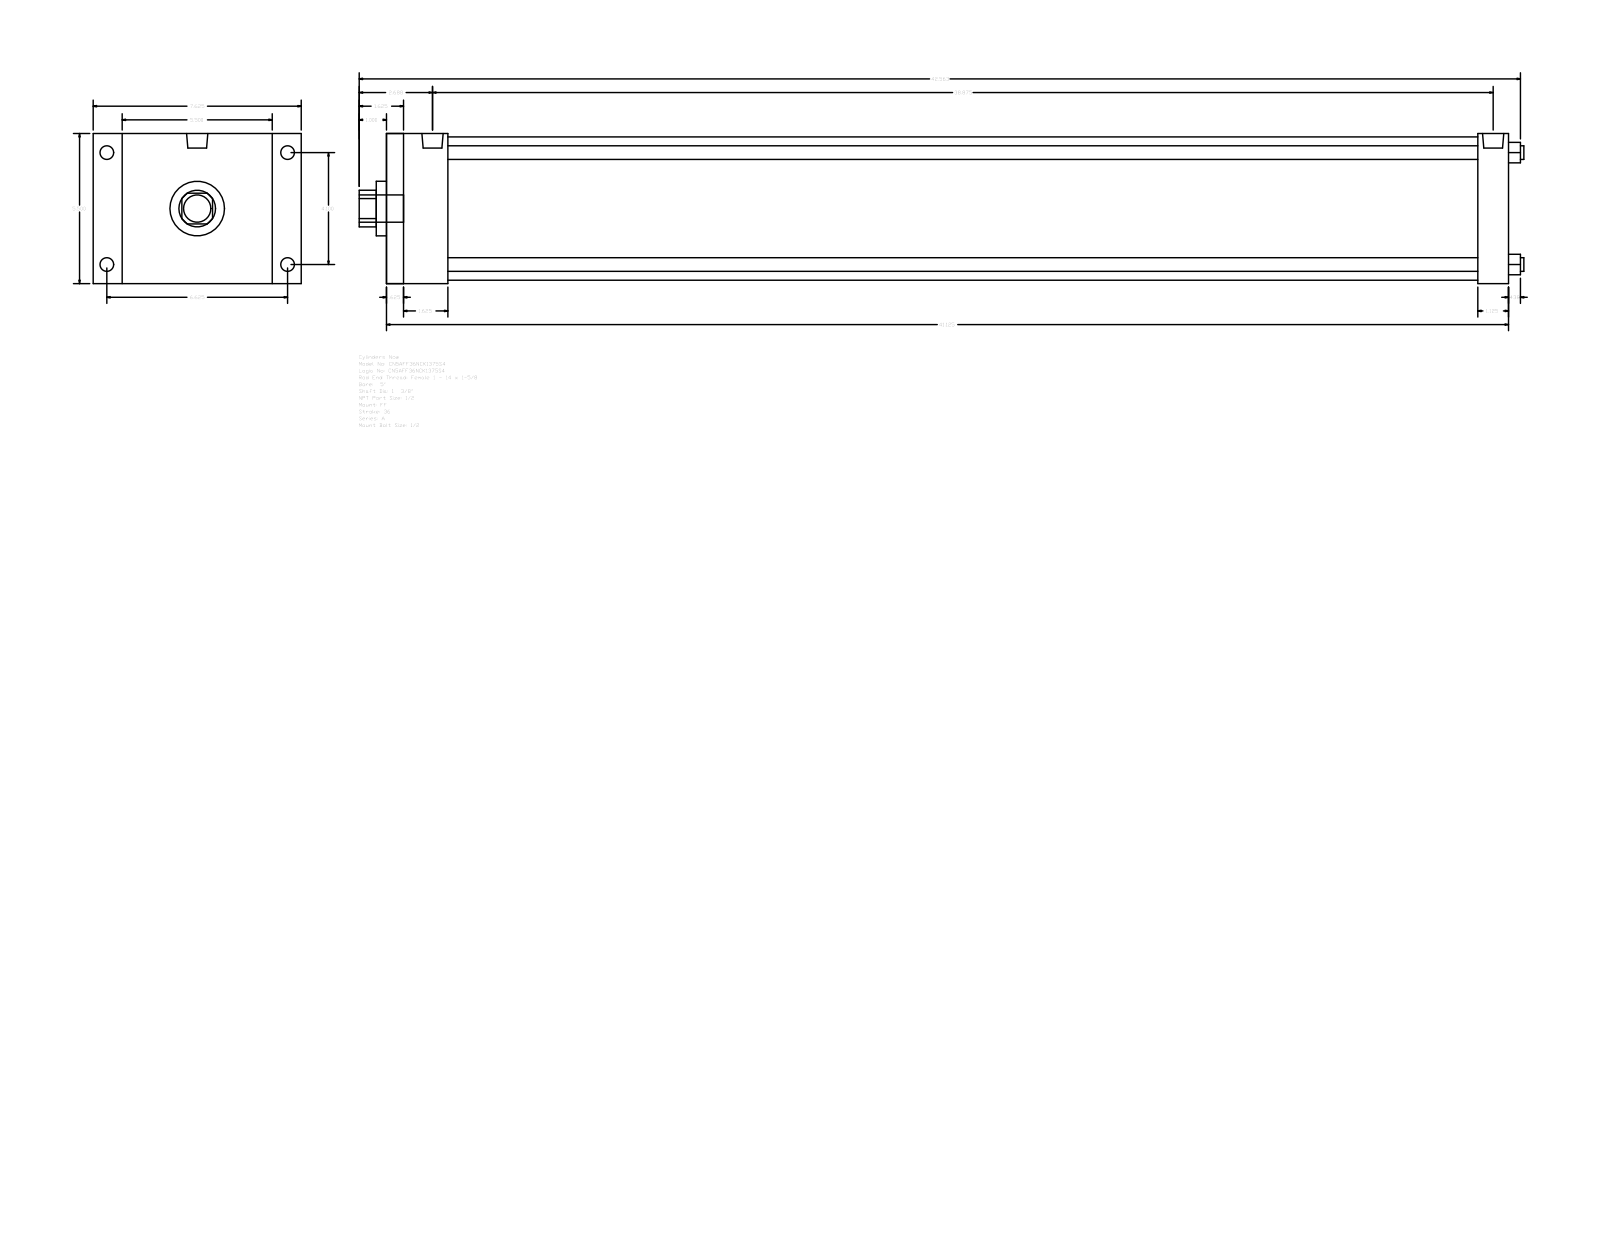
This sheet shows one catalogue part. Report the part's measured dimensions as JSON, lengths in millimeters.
{"part_name": "A_FF__0500_1.375", "step_written_by": "GSSL Pune (CONFIG_CONTROL_DESIGN)", "units": "millimeters", "bodies": {"solids": 0, "faces": 92, "planar": 64, "cylindrical": 28, "other": 0}, "overall_size": [1084.26, 193.68, 139.7], "round_holes": [[12.7, 4], [34.92, 1], [50.8, 1], [133.35, 1]], "round_bosses_or_shafts": [[12.7, 4], [8.73, 4], [19.77, 2], [25.4, 1]], "partial_cylinders_radius": [[17.06, 1]], "face_to_face_distances": [139.7, 1044.57, 1028.7, 15.87, 28.57, 1016, 1000.13, 57.15, 41.28, 958.85], "hole_center_spacings": [73.64, 104.14, 147.28]}
